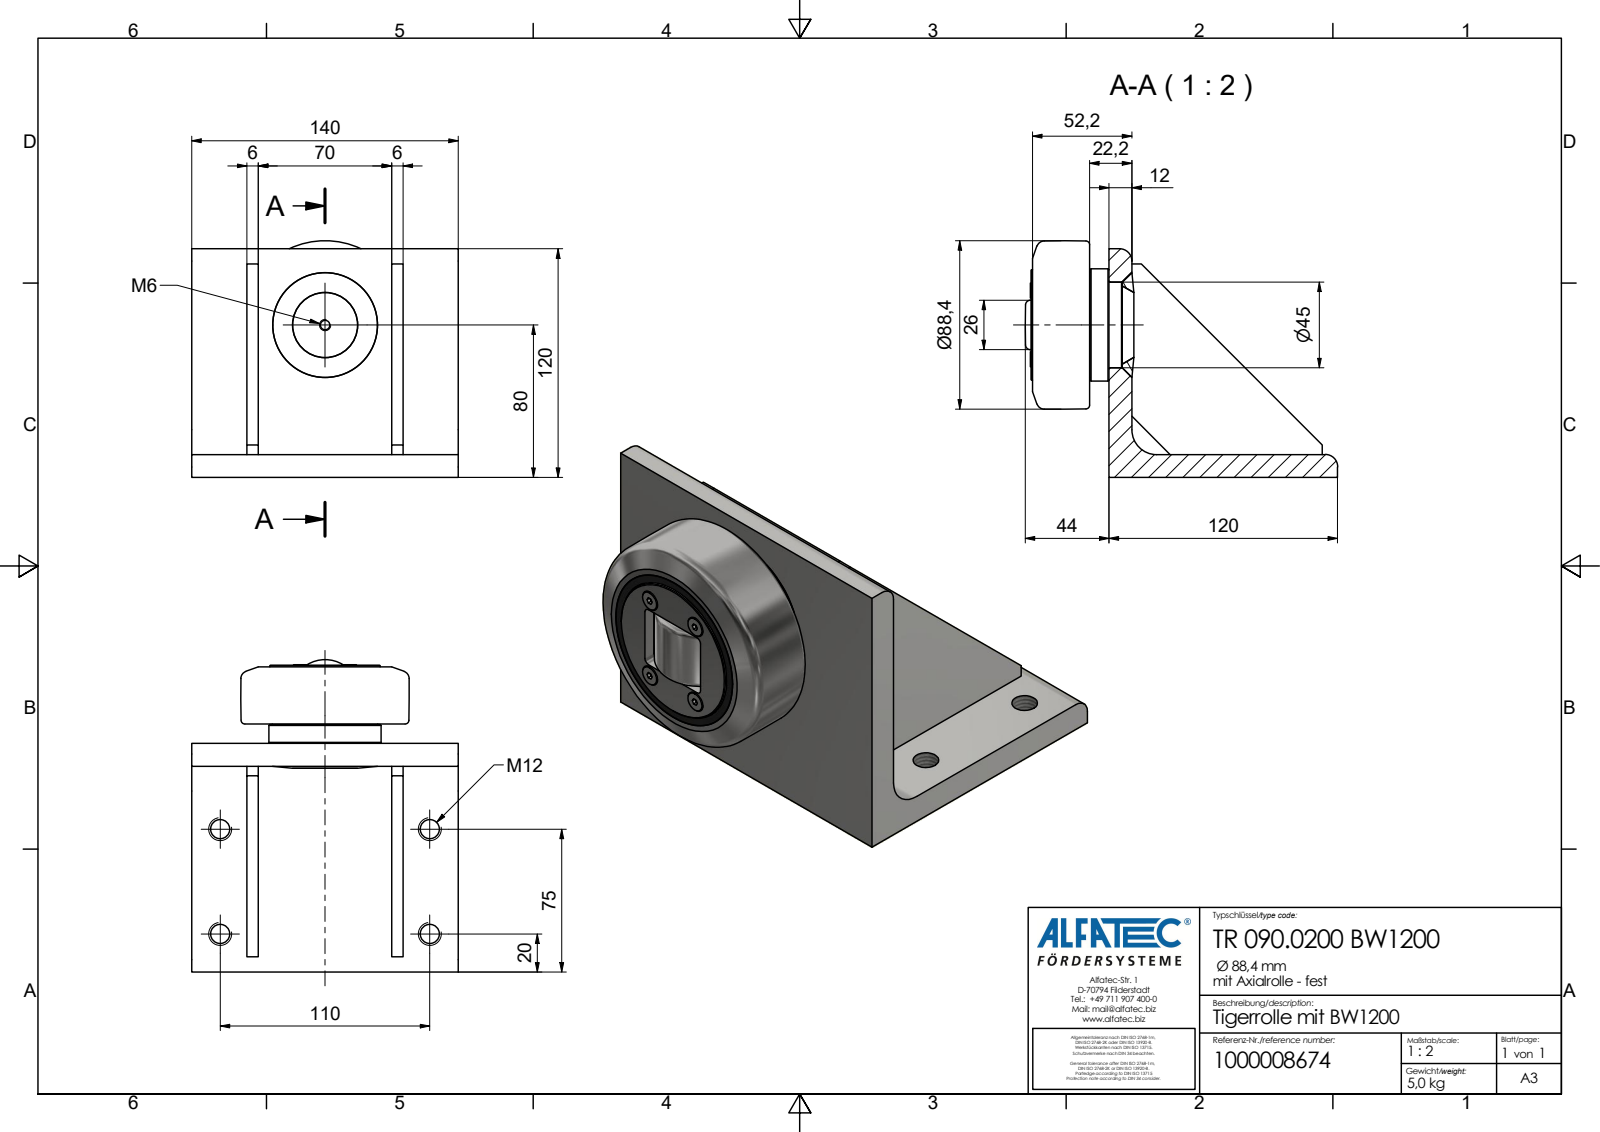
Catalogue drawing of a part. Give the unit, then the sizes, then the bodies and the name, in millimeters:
Units: millimetres
Overall size (bounding box): 164 × 140 × 124.2
Round holes (diameter × count): ⌀10.11 ×4, ⌀2.5 ×1, ⌀4.92 ×1
Round bosses / shafts (diameter × count): ⌀7.8 ×4, ⌀59 ×1, ⌀58 ×1, ⌀55.3 ×1
Partial cylindrical surfaces — rounded edges, fillets, slot ends (radius × count): R2 ×4, R6.5 ×2, R1.5 ×1, R13 ×1, R25 ×1
Main face-to-face distances: 12, 76, 6, 29, 35, 105, 111, 82, 70, 10.2
Hole centre spacings: 55, 110, 122.98
Volume: 656 283 mm³ · Surface area: 110 612 mm²
Bodies: 1 solid, 103 faces (66 planar, 22 cylindrical, 15 other)
Part name (STEP PRODUCT): TR 090.0200 BW1200_Kontur
STEP written by: Autodesk Inventor 2020 (AP242_MANAGED_MODEL_BASED_3D_ENGINEERING_MIM_LF)
